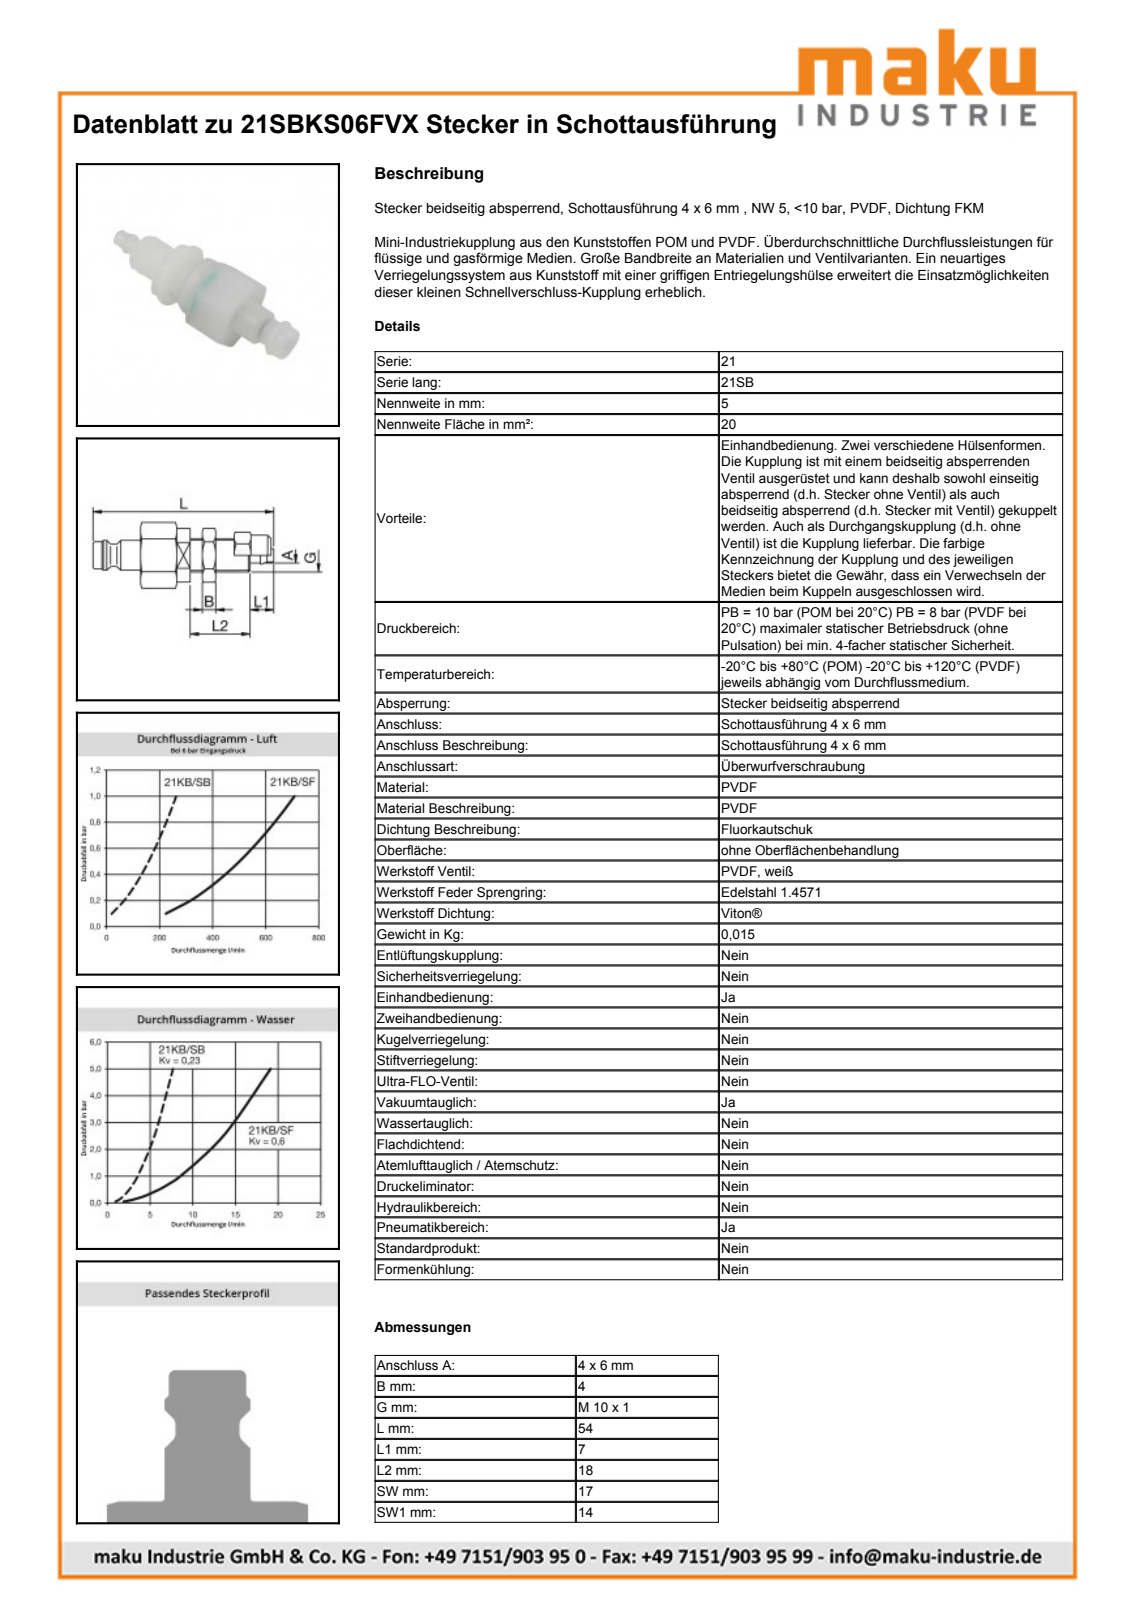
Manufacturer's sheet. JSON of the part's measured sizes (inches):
{"part_name": "D108171", "step_written_by": "Autodesk Inventor 2013 (AUTOMOTIVE_DESIGN)", "units": "inches", "bodies": {"solids": 1, "faces": 337, "planar": 179, "cylindrical": 126, "other": 32}, "overall_size": [2.13, 0.773, 0.669], "volume_in3": 0.398, "surface_area_in2": 5.777, "round_holes": [[0.244, 1], [0.351, 1], [0.451, 1], [0.524, 1]], "round_bosses_or_shafts": [[0.413, 1], [0.368, 1], [0.354, 1], [0.348, 1], [0.345, 1], [0.332, 1], [0.321, 1], [0.262, 1]], "partial_cylinders_radius": [[0.185, 18], [0.01, 6], [0.236, 1], [0.273, 1], [0.315, 1], [0.323, 1]], "face_to_face_distances": [0.669, 0.354, 0.157, 0.512, 0.197, 0.472, 0.781, 0.585, 0.427, 0.315]}
